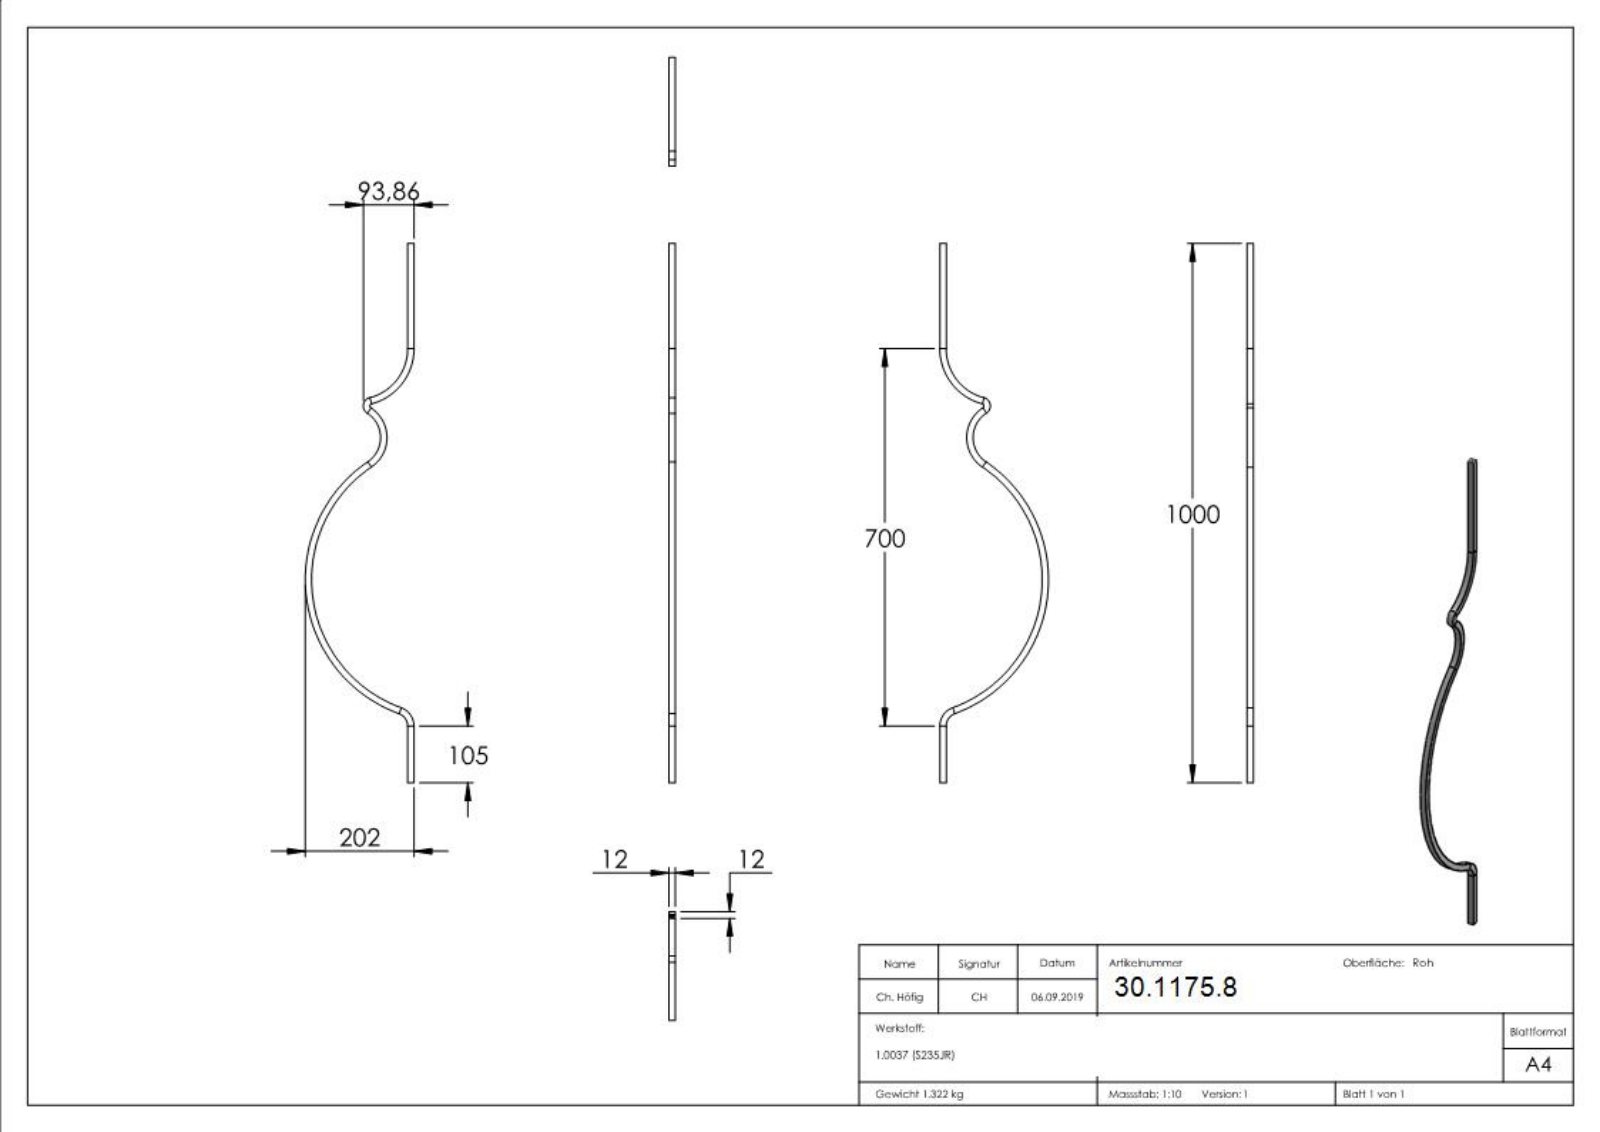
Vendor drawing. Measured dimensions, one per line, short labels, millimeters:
name: 1731-G
written by: SolidWorks 2015 (CONFIG_CONTROL_DESIGN)
unit: mm
bodies: 1 solid, 188 faces (110 planar, 16 cylindrical, 62 other)
size: 1000 × 202 × 12
volume: 169 550 mm³; area: 56 811 mm²
rounds: 1× R4, 1× R16, 1× R24, 1× R36, 1× R54, 1× R66, 1× R94, 1× R106
face distances: 12, 1000, 999.9, 3.74, 0.57, 2.7, 3.66, 3.85, 6, 2.97
